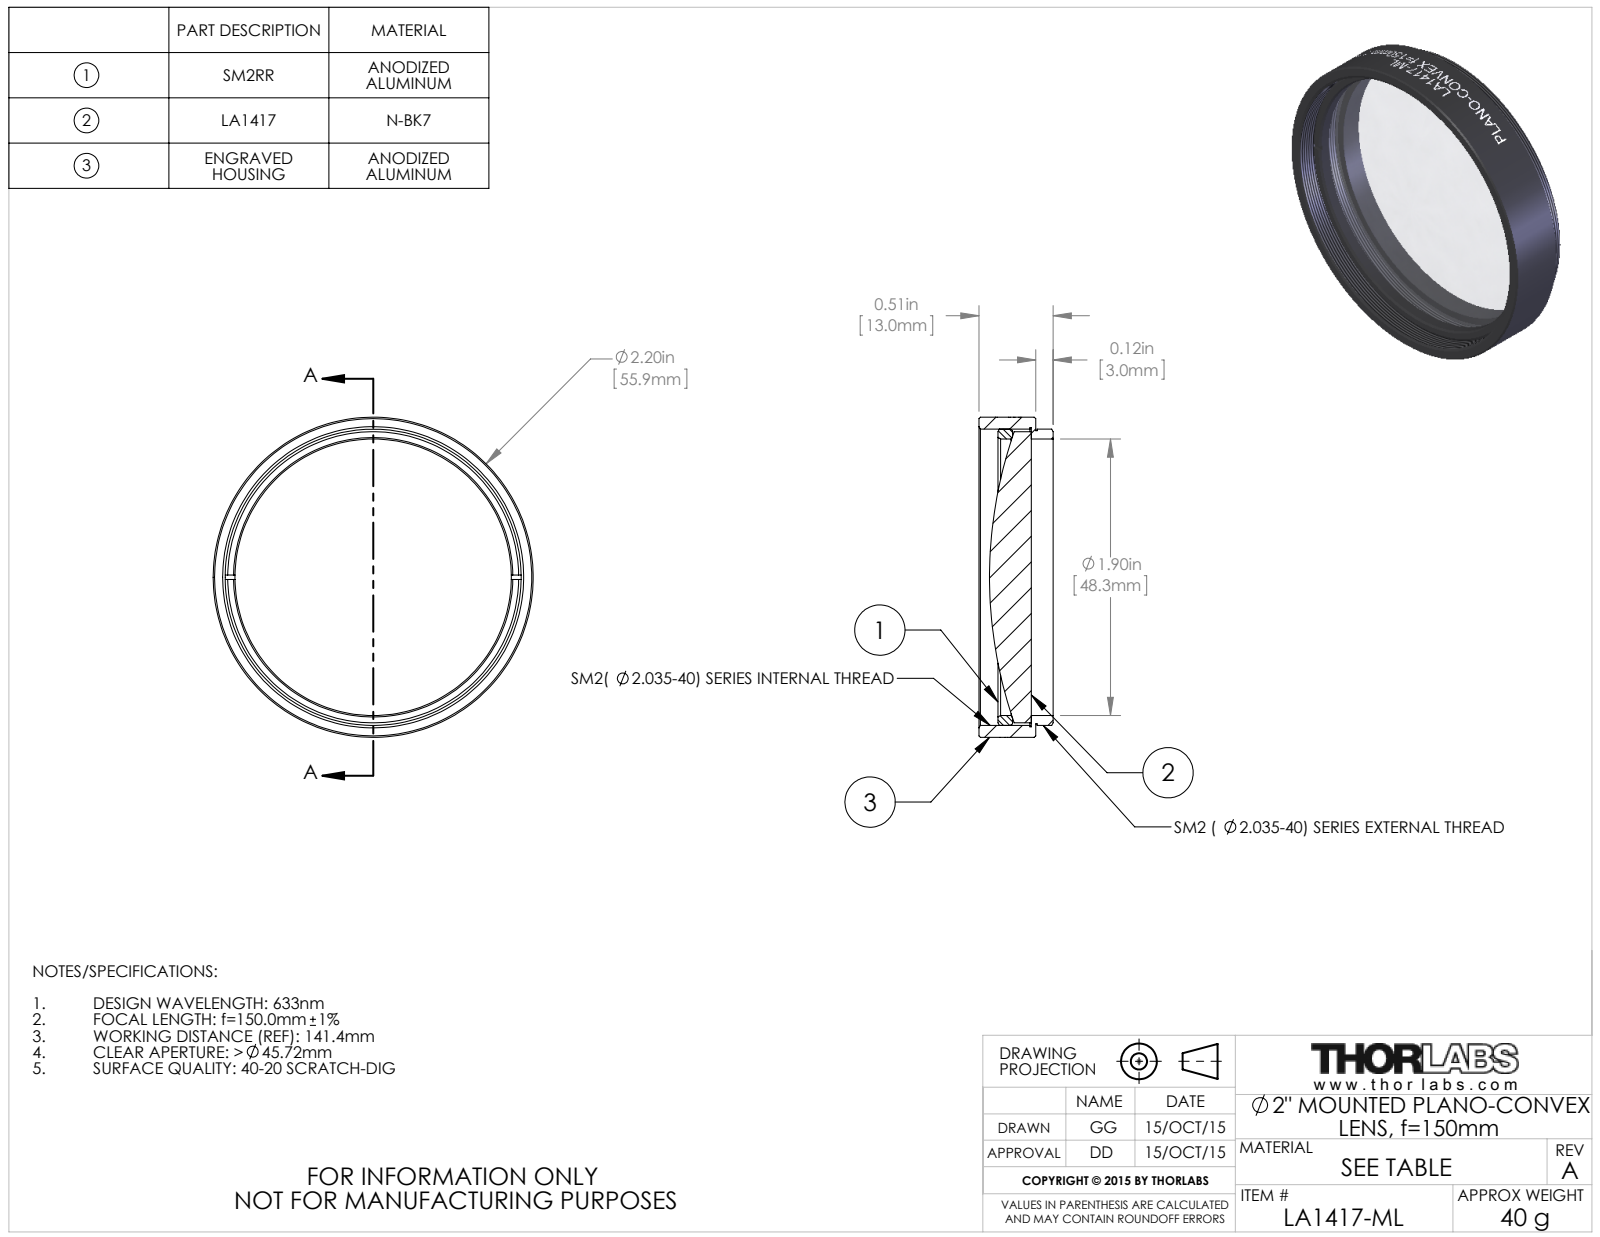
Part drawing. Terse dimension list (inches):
name: TTN039582-E0W
written by: SolidWorks 2014 (CONFIG_CONTROL_DESIGN)
unit: in
bodies: 3 solids, 107 faces (16 planar, 71 cylindrical, 20 other)
size: 2.2 × 2.2 × 0.51
volume: 0.952 in³; area: 17.68 in²
holes: 1× ⌀1.9, 1× ⌀2.055
bosses: 1× ⌀2.2, 1× ⌀2.035, 1× ⌀2.015, 1× ⌀2
face distances: 0.03, 0.39, 0.36, 0.12, 0.15, 0.51, 0.279, 0.159, 0.129, 0.231
